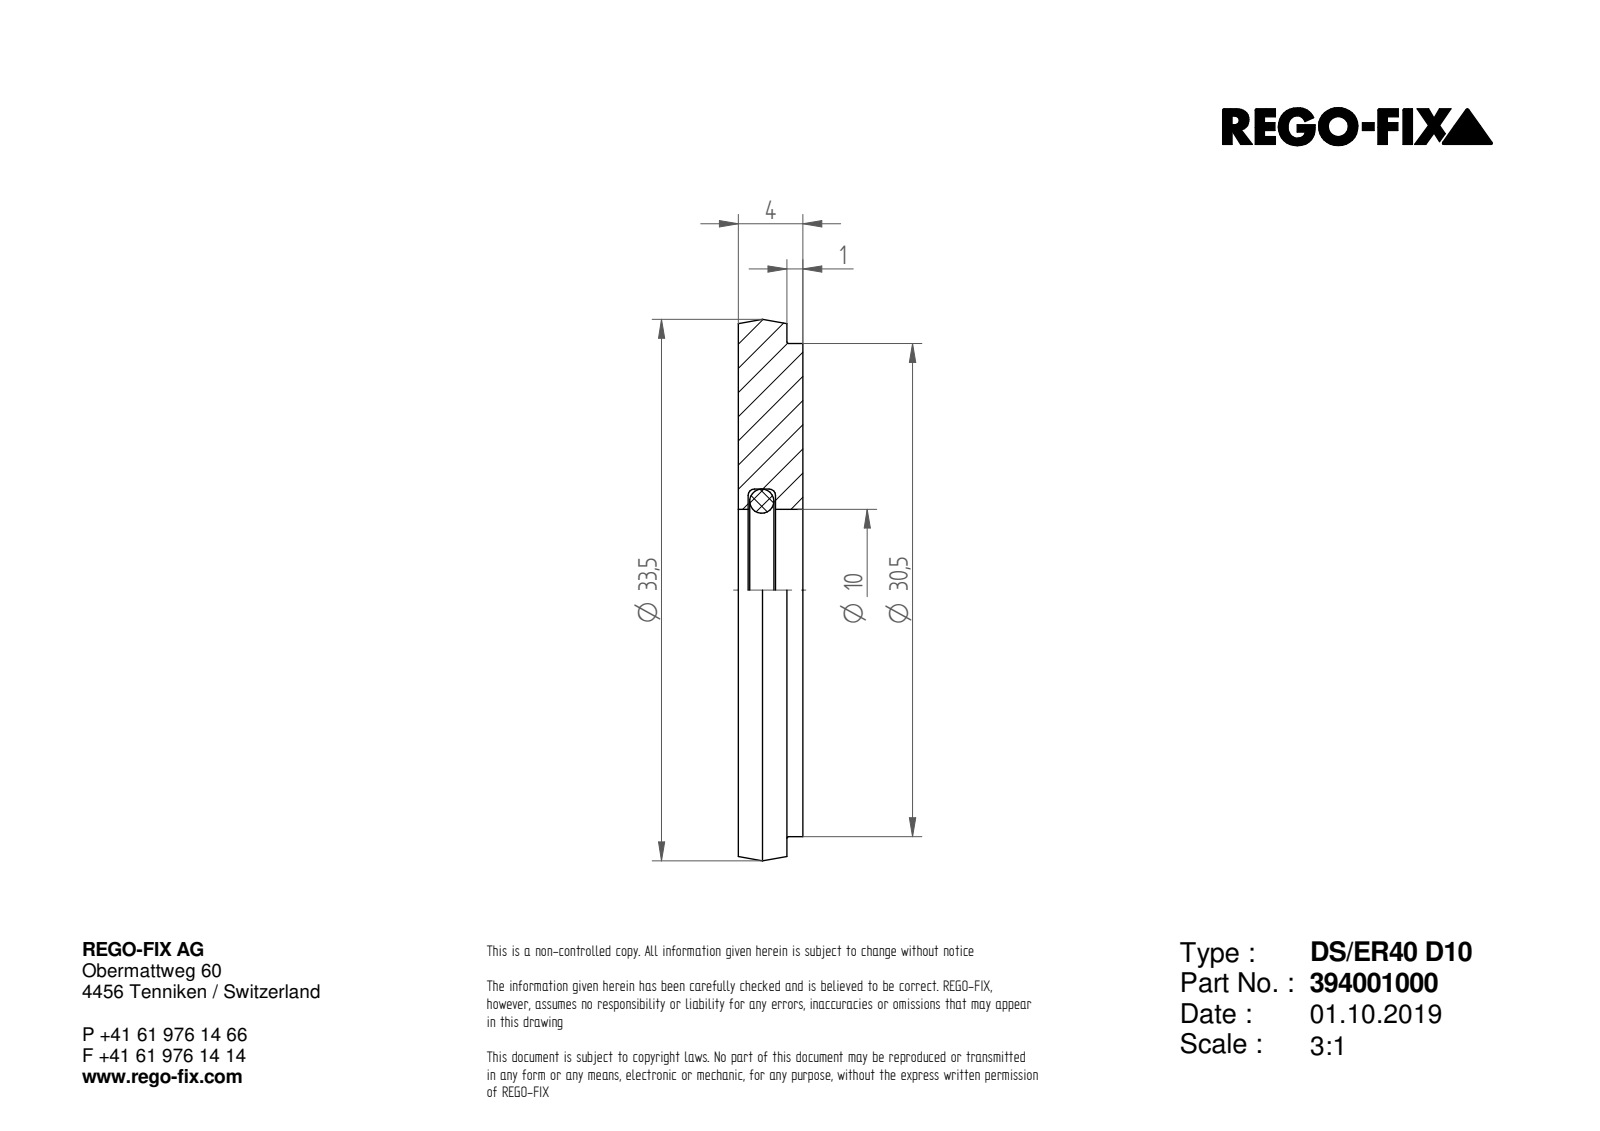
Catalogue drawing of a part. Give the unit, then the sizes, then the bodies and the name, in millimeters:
Units: millimetres
Overall size (bounding box): 33.5 × 33.5 × 4
Round holes (diameter × count): ⌀10 ×1
Round bosses / shafts (diameter × count): ⌀33.5 ×1, ⌀30.5 ×1
Main face-to-face distances: 4, 1, 3
Volume: 3 061 mm³ · Surface area: 2 139 mm²
Bodies: 1 solid, 7 faces (3 planar, 3 cylindrical, 1 other)
Part name (STEP PRODUCT): NOCUT
STEP written by: SIEMENS PLM Software Solid Edge ST10 (AUTOMOTIVE_DESIGN)
